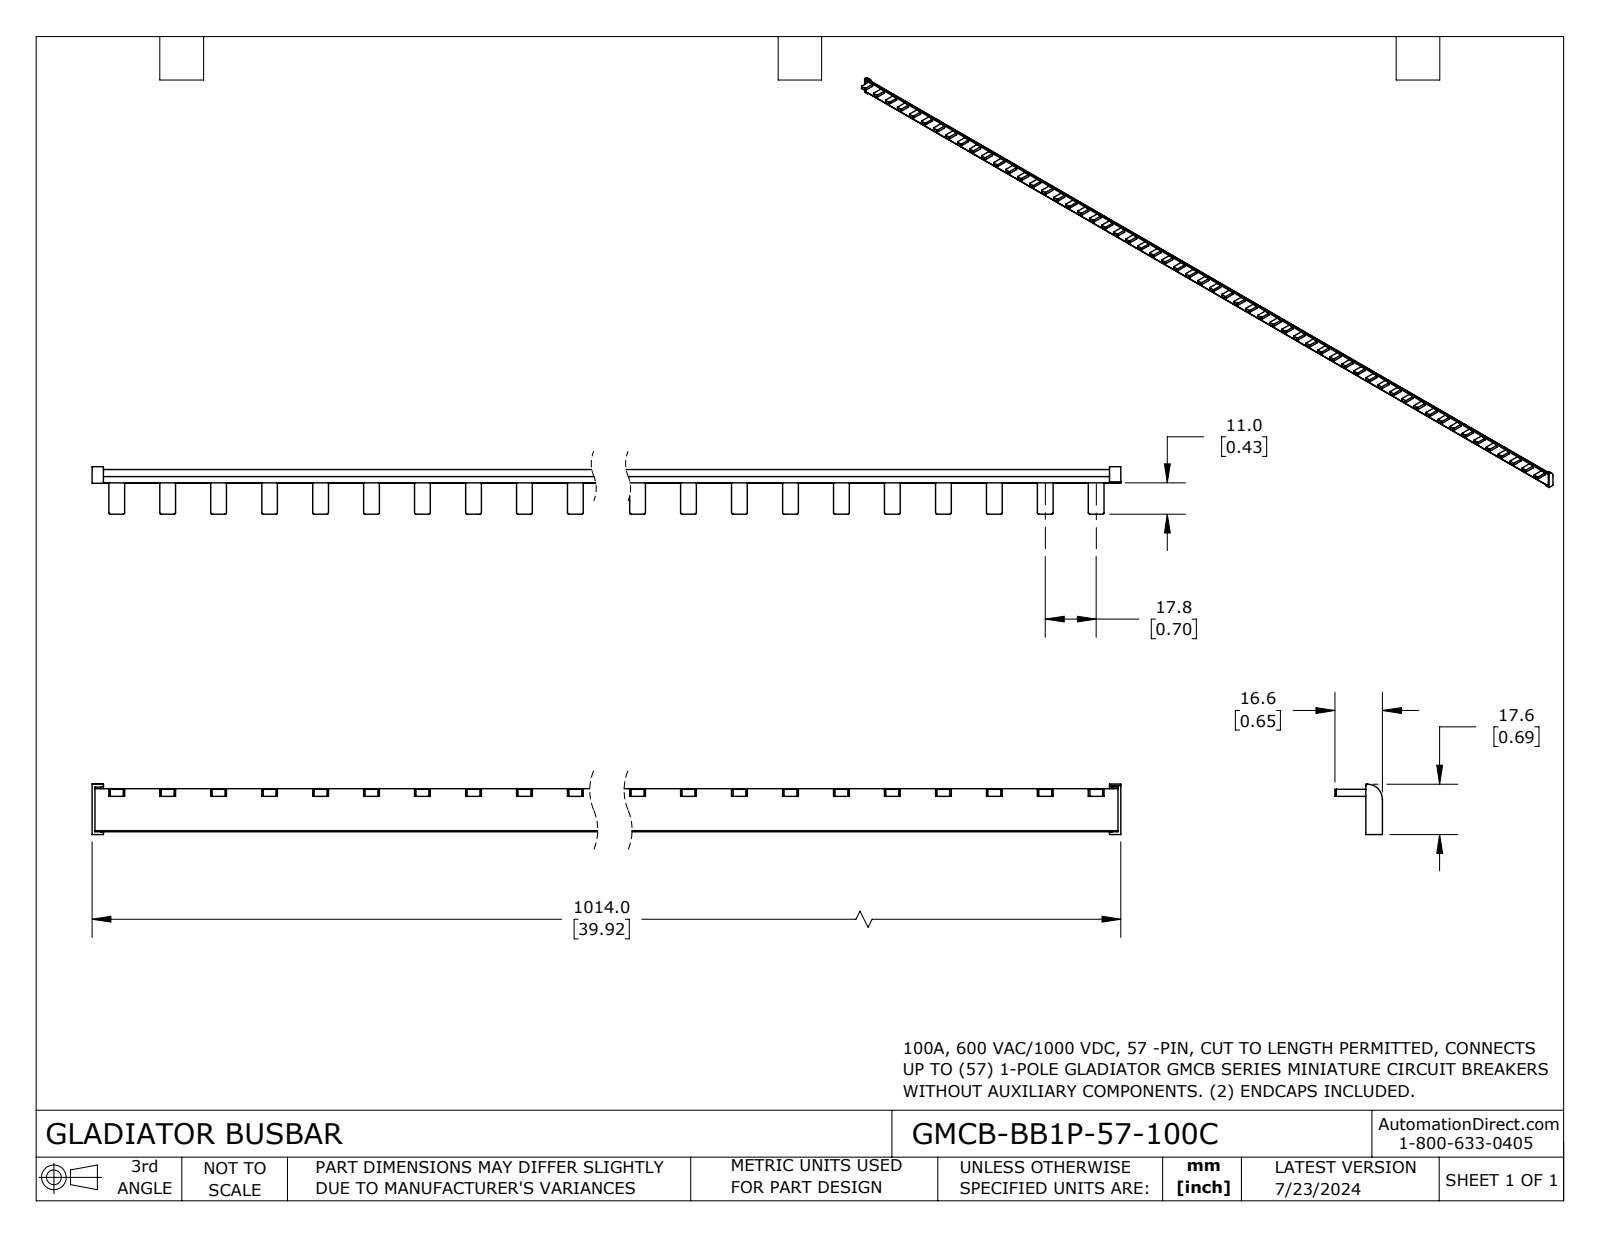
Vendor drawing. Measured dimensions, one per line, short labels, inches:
name: GMCB-BB1P-57-100C
written by: SolidWorks 2023 (CONFIG_CONTROL_DESIGN)
unit: in
bodies: 1 solid, 440 faces (314 planar, 124 cylindrical, 2 other)
size: 39.921 × 0.693 × 0.654
volume: 4.673 in³; area: 75.45 in²
rounds: 115× R0.02, 2× R0.169, 1× R0.165, 1× R0.209
face distances: 0.183, 0.484, 0.583, 0.098, 0.591, 0.106, 0.431, 0.614, 1.402, 2.803
